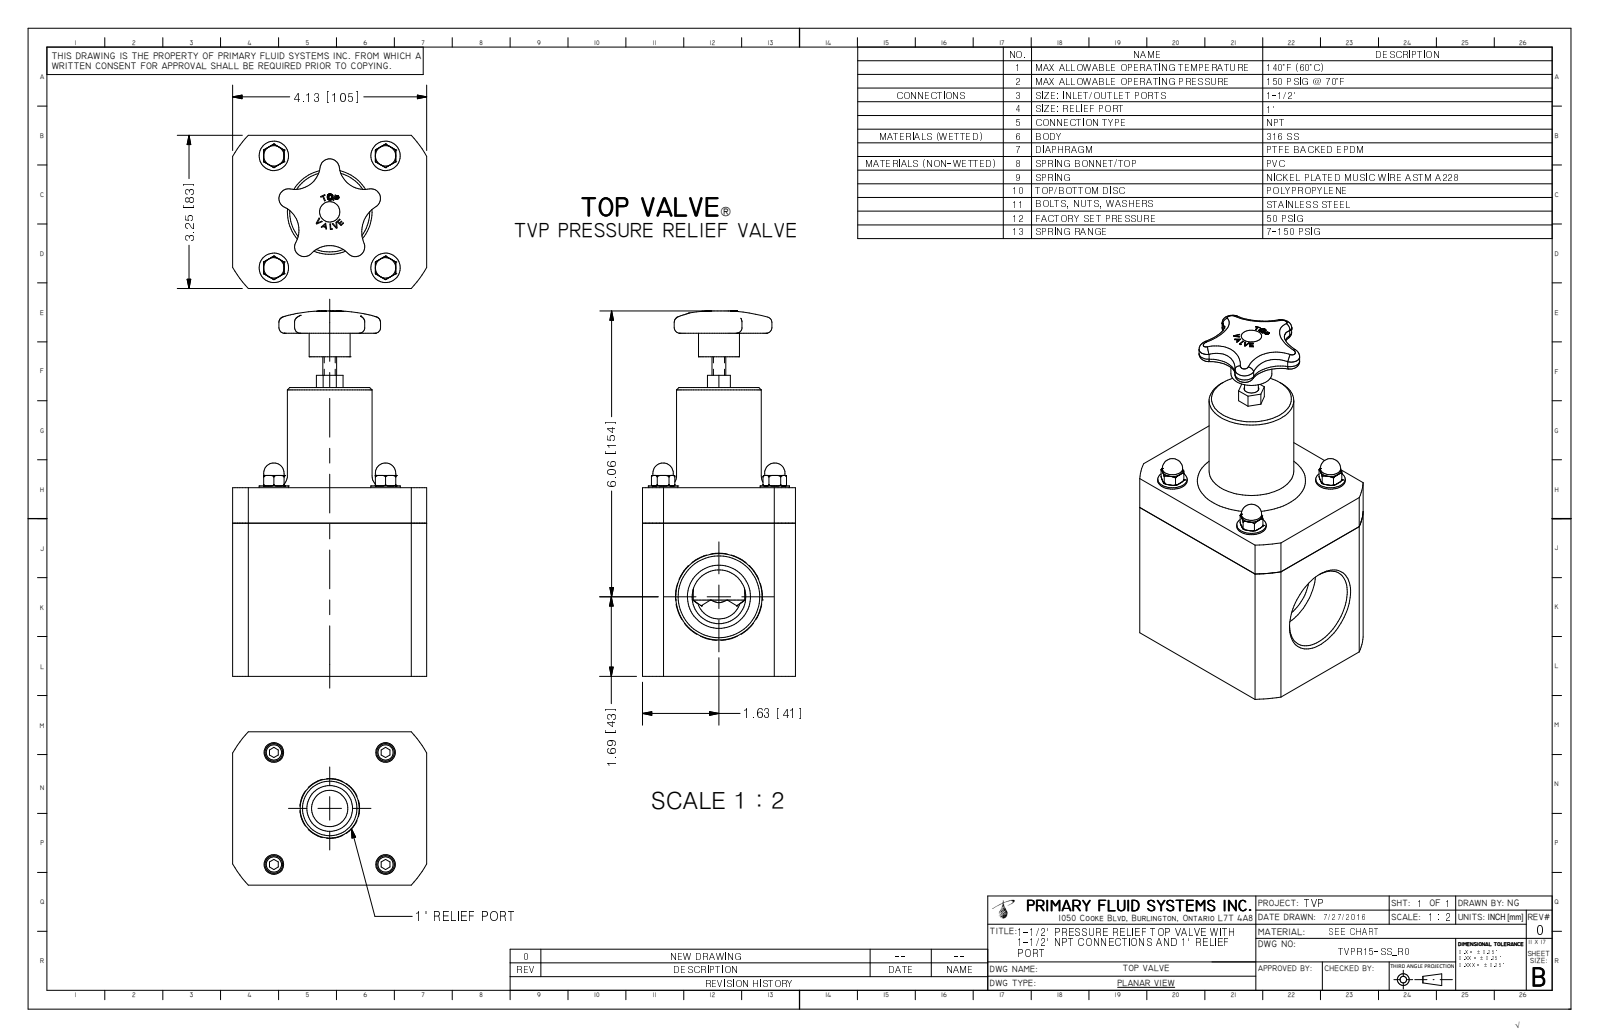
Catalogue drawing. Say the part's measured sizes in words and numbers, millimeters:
The part is named "TVPR15-SS_R0". Its 3-D file was written by "Autodesk Inventor 2009 (AUTOMOTIVE_DESIGN)". It is 1 solid with 340 faces: 145 planar, 46 cylindrical and 149 other. Overall it measures 196.9 by 104.8 by 82.6 millimeters. Its volume is 886 700 cubic millimeters and its surface area 78 650 square millimeters. Round holes: 4 of diameter 4.4, 1 of diameter 29.4, 1 of diameter 44. Round bosses or shafts: 4 of diameter 15.9, 4 of diameter 11, 4 of diameter 9.5, 1 of diameter 45.7, 1 of diameter 22.1, 1 of diameter 7.4. Partial cylindrical surfaces (rounded edges, fillets, slot ends): 5 of radius 2.2, 5 of radius 5.2, 4 of radius 13.6, 4 of radius 16.7, 1 of radius 15.9, 1 of radius 18.9, 1 of radius 60.3. The main face-to-face distances are 82.6, 101.6, 104.8, 25.4, 79.4, 54, 155.6, 15.2, 86.4, 140.3. The hole center spacings are 42.6, 42.7, 60.3, 60.3, 85.3.
